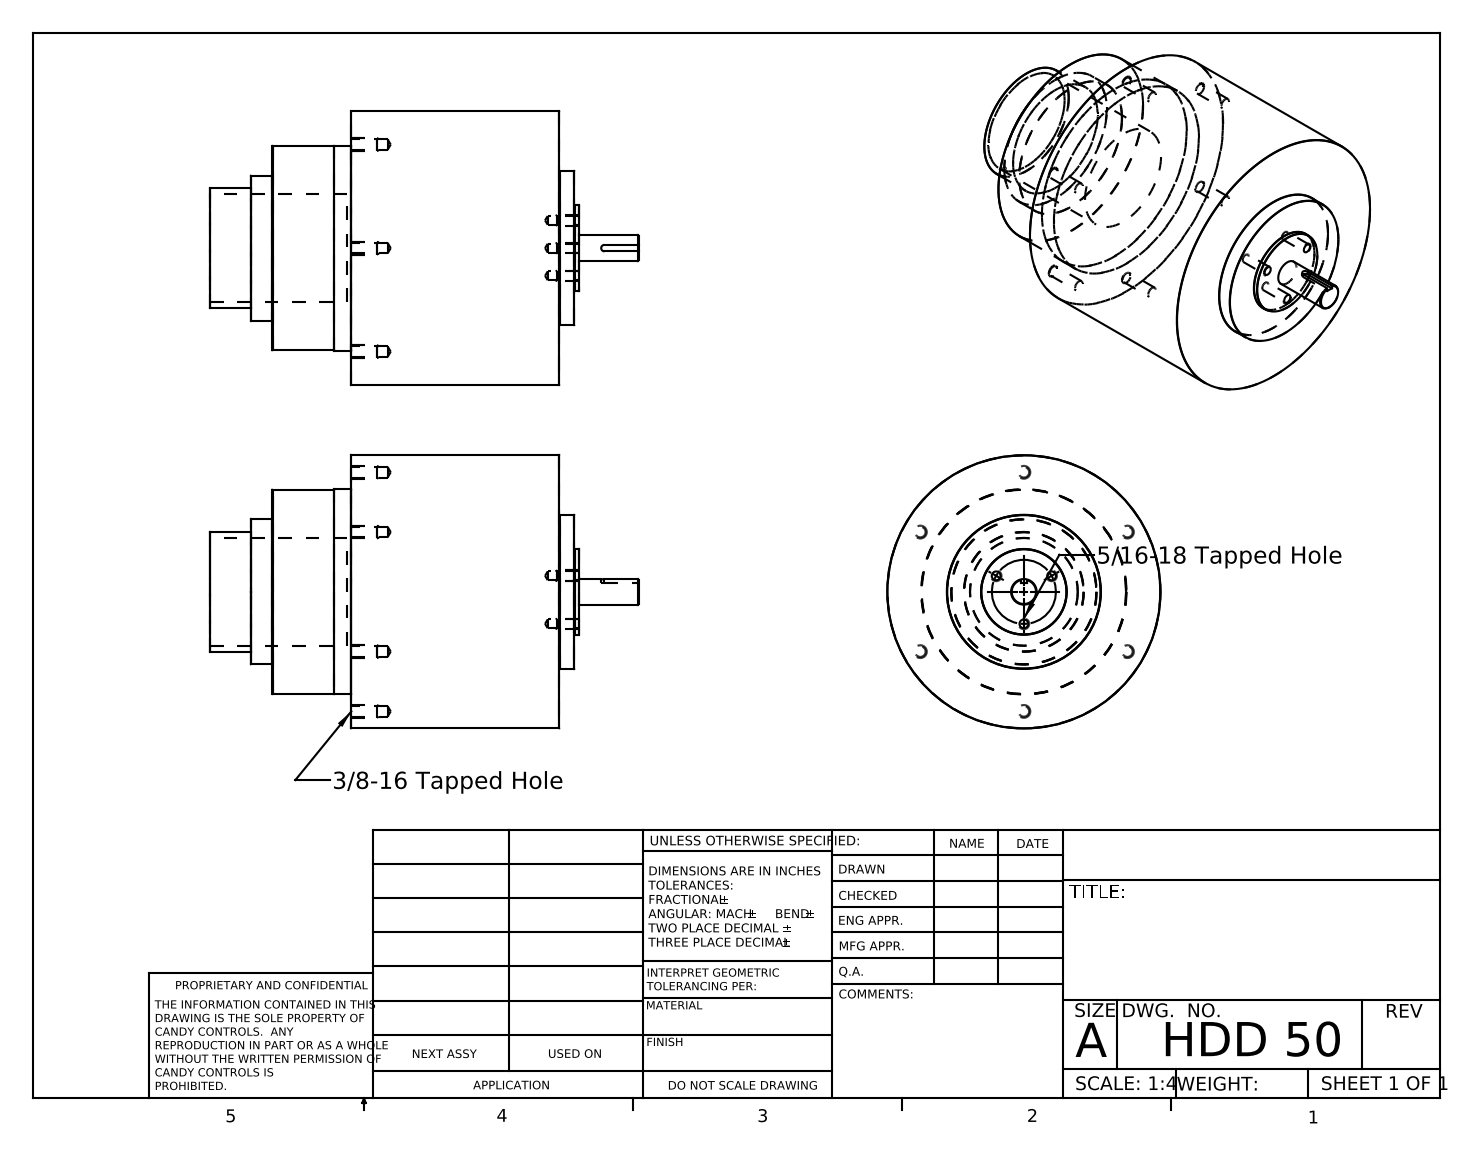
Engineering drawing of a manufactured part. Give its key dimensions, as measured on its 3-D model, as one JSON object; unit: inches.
{"part_name": "HDD 50", "step_written_by": "SolidWorks 2010 (CONFIG_CONTROL_DESIGN)", "units": "inches", "bodies": {"solids": 1, "faces": 98, "planar": 12, "cylindrical": 37, "other": 49}, "overall_size": [12.55, 8, 8], "volume_in3": 368.3, "surface_area_in2": 377.9, "round_holes": [[0.313, 6], [0.257, 3], [3.15, 1]], "round_bosses_or_shafts": [[8, 1], [6, 1], [5.99, 1], [4.5, 1], [4.25, 1], [3.5, 1], [2.5, 1], [0.75, 1]], "partial_cylinders_radius": [[0.094, 1]], "face_to_face_distances": [6.09, 2.31, 8.4, 8.84, 6.53, 0.44, 2.17, 0.14, 6.23, 6.67], "hole_center_spacings": [3.5, 6.062, 3.138, 4.051, 0.937, 1.624, 2.563, 4.437]}
